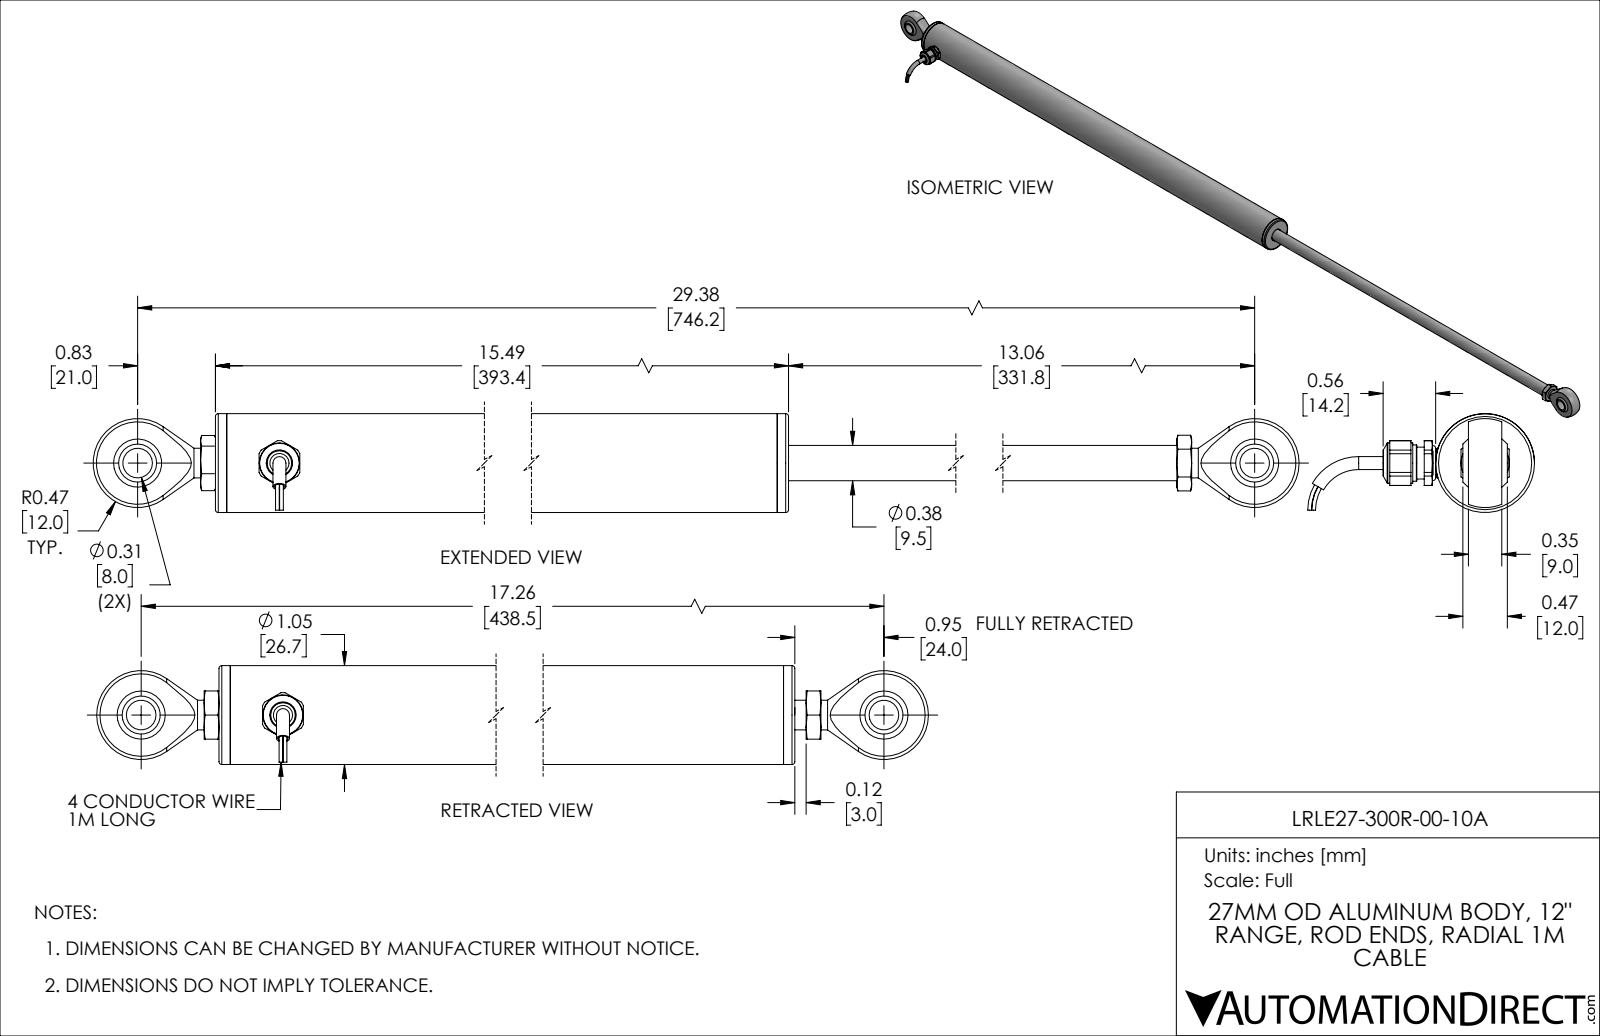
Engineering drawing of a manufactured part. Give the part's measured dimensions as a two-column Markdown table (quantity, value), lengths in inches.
| quantity | value |
| --- | --- |
| part name | LRLE27-300R-00-10A |
| STEP written by | SolidWorks 2019 (AUTOMOTIVE_DESIGN) |
| units | inches |
| bodies | 28 solids, 298 faces (114 planar, 92 cylindrical, 92 other) |
| overall size | 18.088 × 2.409 × 1.05 |
| volume | 8.057 in³ |
| surface area | 164.2 in² |
| round holes (diameter × count) | 0.268 × 2, 0.315 × 2, 0.106 × 1, 0.138 × 1, 0.156 × 1, 0.187 × 1, 0.201 × 1, 0.205 × 1, 0.272 × 1, 0.275 × 1, 0.313 × 1, 0.36 × 1 |
| round bosses / shafts (diameter × count) | 0.039 × 4, 0.315 × 2, 1.05 × 1, 0.85 × 1, 0.848 × 1, 0.685 × 1, 0.625 × 1, 0.5 × 1 |
| partial cylindrical surfaces (radius × count) | 0.01 × 2, 0.067 × 2, 0.25 × 2, 0.197 × 1, 0.224 × 1, 0.238 × 1, 0.344 × 1, 0.407 × 1 |
| main face-to-face distances | 0.354, 15.49, 0.737, 14.753, 0.12, 15.37, 0.5, 1.65, 0.913, 13.84 |
| hole center spacings | 1.507, 15.637, 17.144 |
